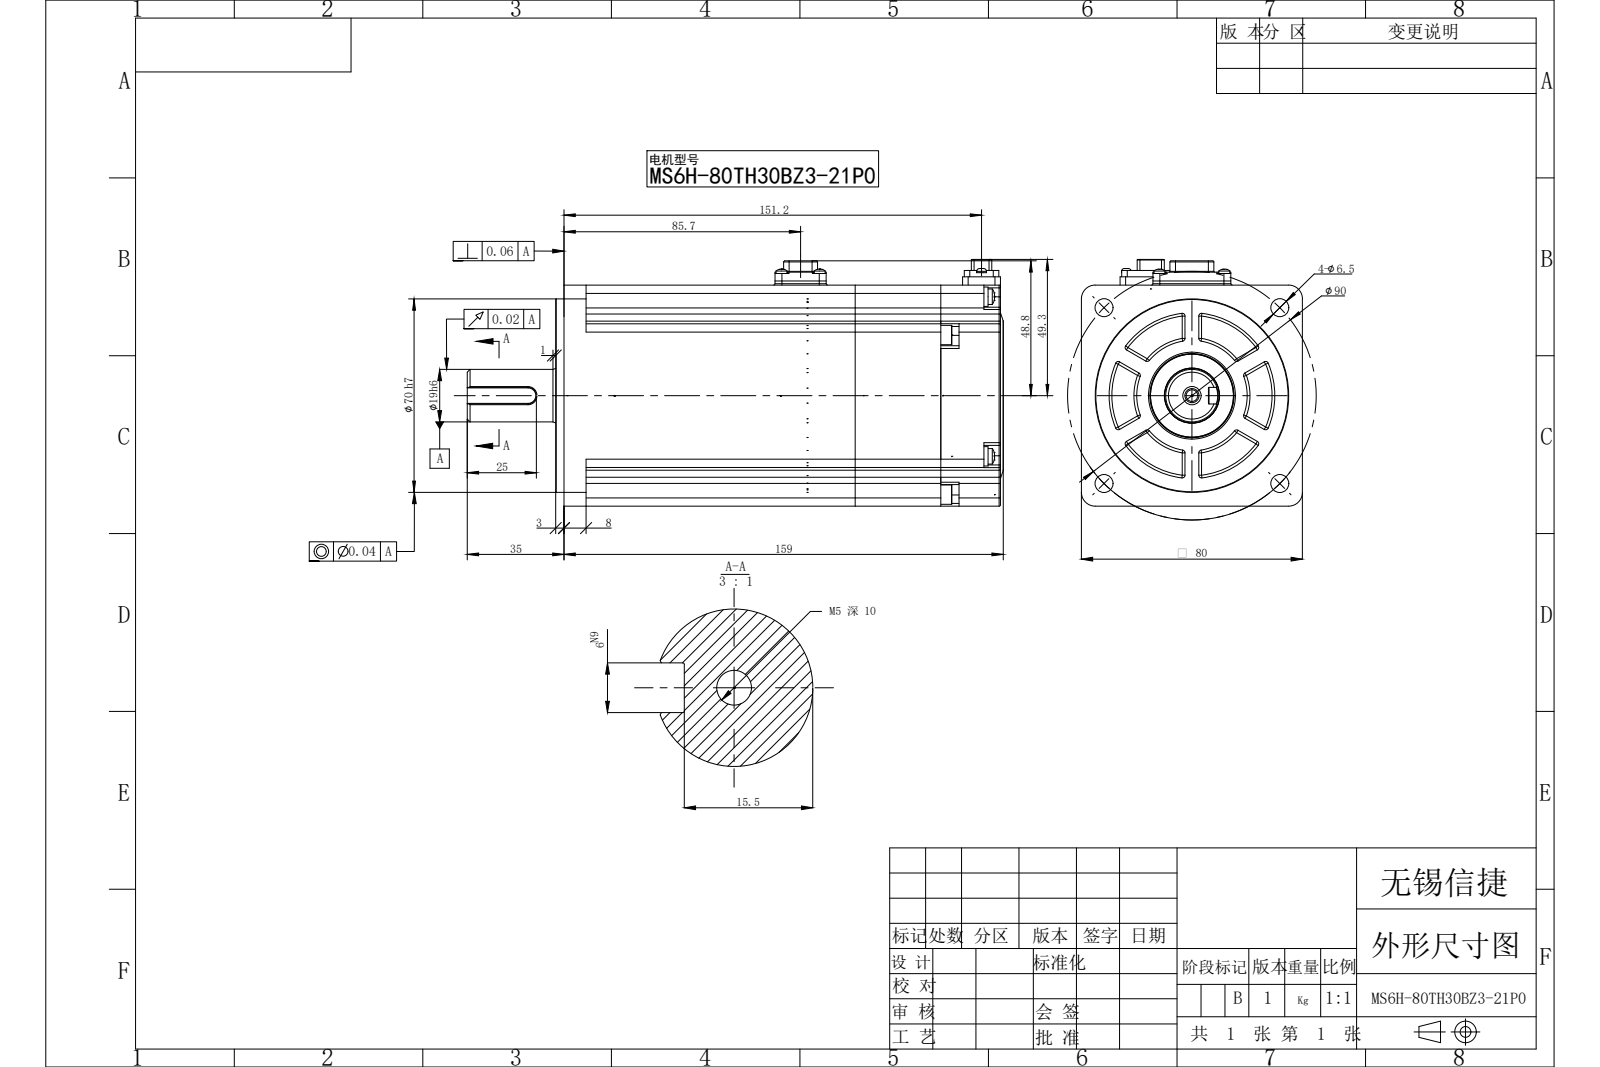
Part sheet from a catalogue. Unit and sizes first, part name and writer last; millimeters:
Units: millimetres
Overall size (bounding box): 194 × 89.3 × 80
Round holes (diameter × count): ⌀2.1 ×4, ⌀6.5 ×4, ⌀1.6 ×2, ⌀4.2 ×1, ⌀20 ×1
Round bosses / shafts (diameter × count): ⌀7 ×8, ⌀5.6 ×4, ⌀4 ×4, ⌀3.5 ×2, ⌀70 ×1, ⌀30 ×1, ⌀19.8 ×1, ⌀19 ×1
Partial cylindrical surfaces — rounded edges, fillets, slot ends (radius × count): R1 ×50, R0.5 ×27, R3 ×17, R0.2 ×14, R2 ×12, R0.3 ×10, R3.75 ×8, R0.6 ×4
Main face-to-face distances: 80, 66, 14, 52, 158, 1, 159, 3, 162, 161
Hole centre spacings: 45, 63.64, 8, 16.6, 18.43, 90, 23.5, 61.72
Bodies: 0 solids, 795 faces (358 planar, 291 cylindrical, 146 other)
Part name (STEP PRODUCT): MS6H-80TH30BZ3-21P0
STEP written by: SolidWorks 2022 (CONFIG_CONTROL_DESIGN)
